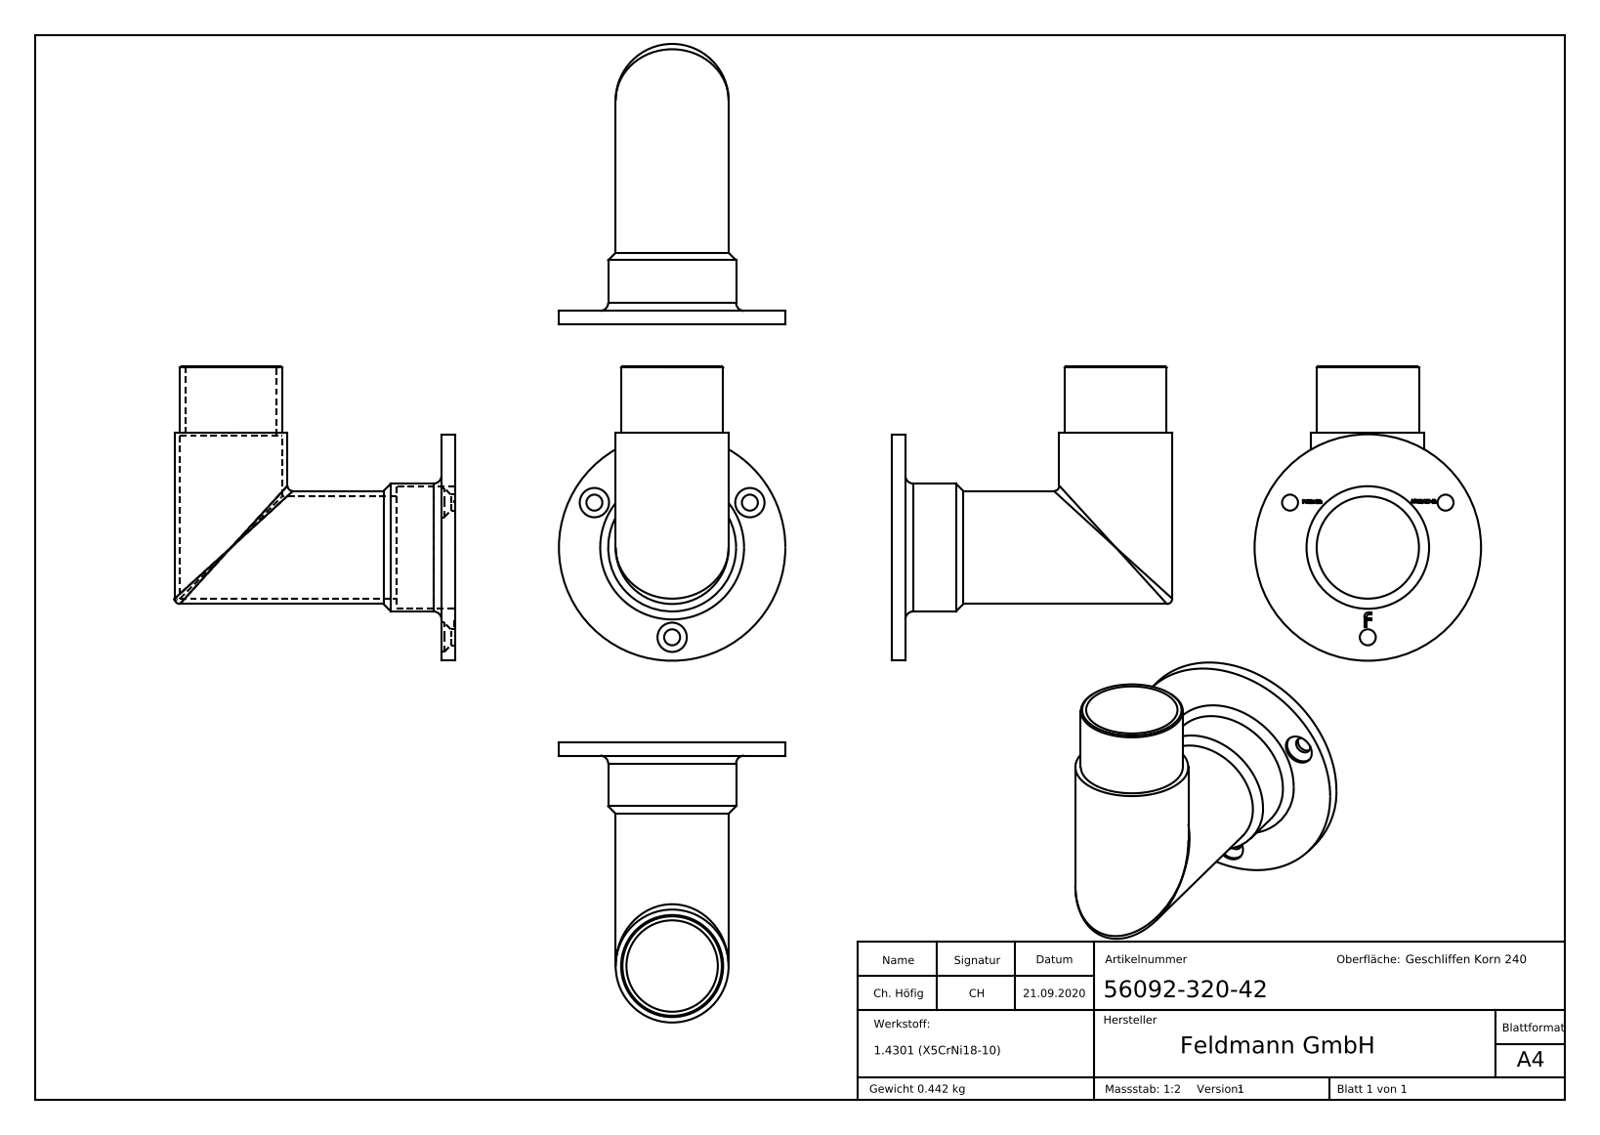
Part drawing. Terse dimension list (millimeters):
name: 56092-320-42
written by: SolidWorks 2018 (CONFIG_CONTROL_DESIGN)
unit: mm
bodies: 1 solid, 302 faces (153 planar, 15 cylindrical, 134 other)
size: 110.5 × 105.2 × 85
volume: 55 937 mm³; area: 48 589 mm²
holes: 3× ⌀6, 3× ⌀11, 2× ⌀38.4, 1× ⌀34.3, 1× ⌀46
bosses: 2× ⌀42.4, 1× ⌀85, 1× ⌀48, 1× ⌀38.3
face distances: 5, 22, 17, 1, 26, 25, 4.9, 21.9, 0.91, 25.15
hole spacings: 33.7, 58.37, 58.38
